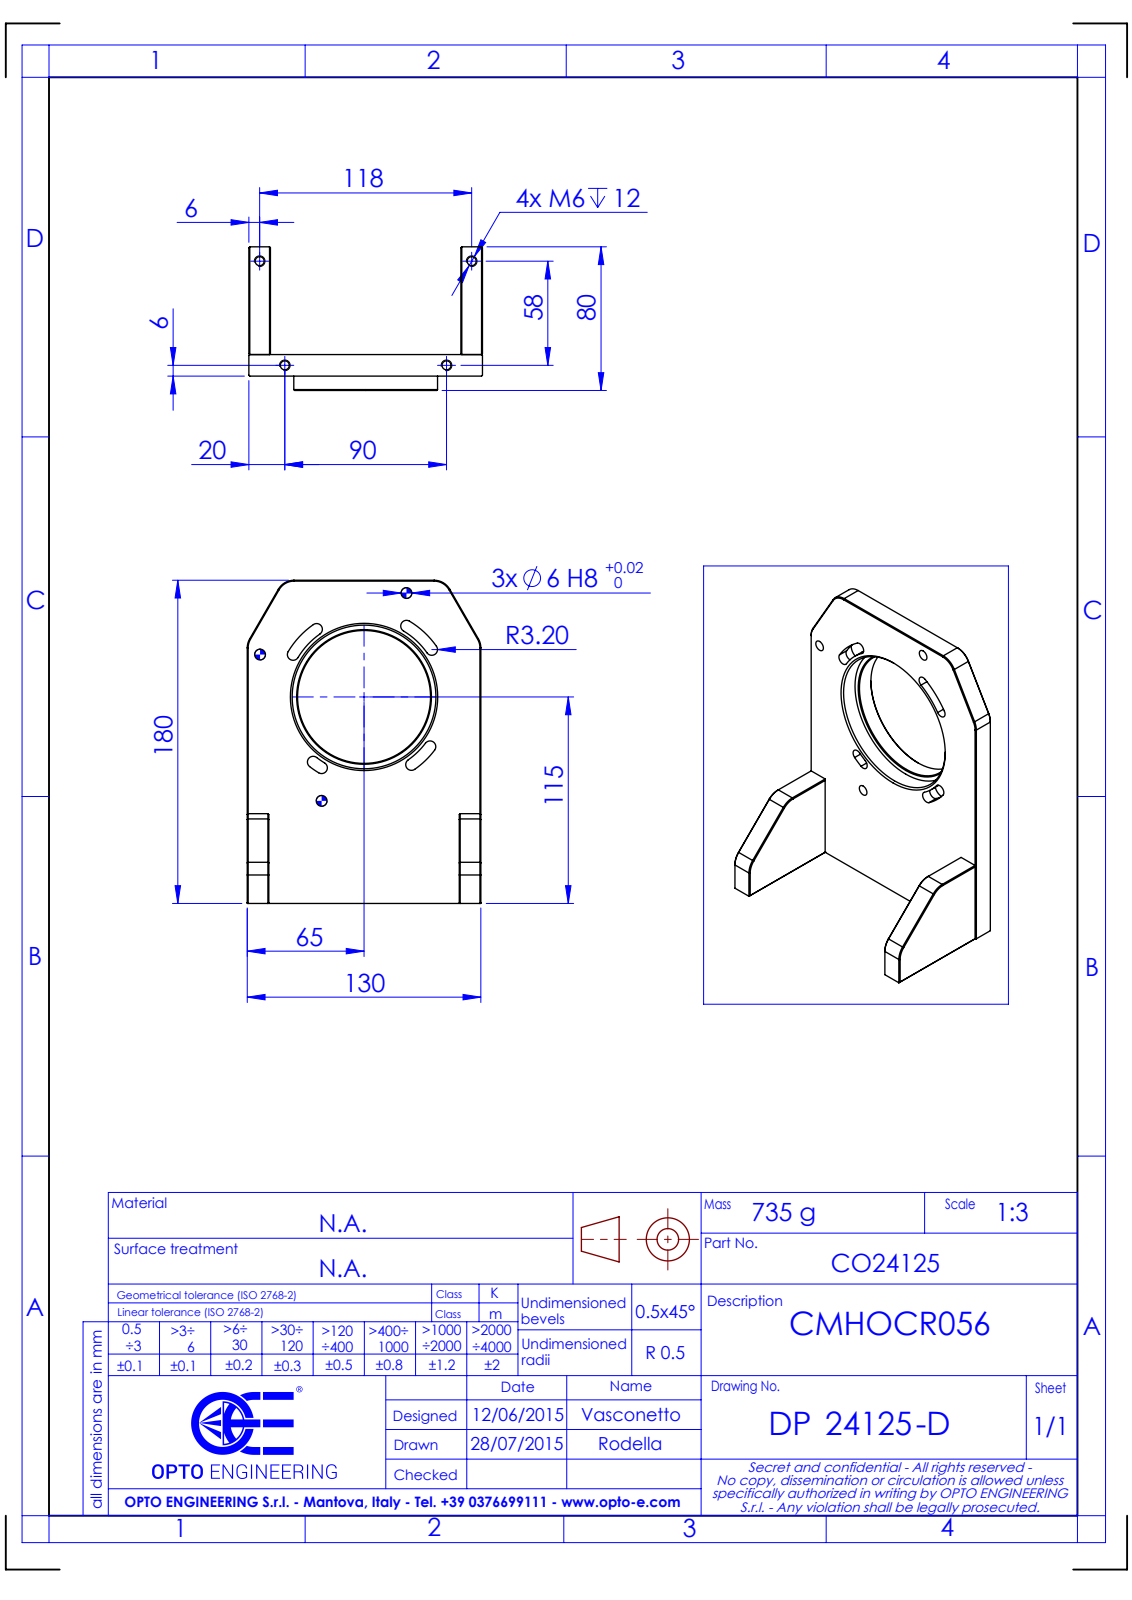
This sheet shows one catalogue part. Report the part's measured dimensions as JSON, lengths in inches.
{"part_name": "DP24125-D_CMHOCR056", "step_written_by": "SolidWorks 2021 (CONFIG_CONTROL_DESIGN)", "units": "inches", "bodies": {"solids": 0, "faces": 206, "planar": 82, "cylindrical": 84, "other": 40}, "overall_size": [7.087, 5.118, 3.15], "round_holes": [[0.197, 4], [0.433, 4], [0.236, 3], [2.913, 1], [3.15, 1]], "round_bosses_or_shafts": [[0.394, 4]], "partial_cylinders_radius": [[0.126, 8], [0.217, 8], [0.394, 6], [1.594, 1], [1.685, 1], [1.937, 1], [2.028, 1]], "face_to_face_distances": [0.472, 4.646, 5.118, 4.173, 0.394, 7.087, 0.079, 1.969, 0.787, 0.252], "hole_center_spacings": [2.461, 4.646, 1.181, 2.349, 3.48, 3.757, 4.688, 4.742]}
